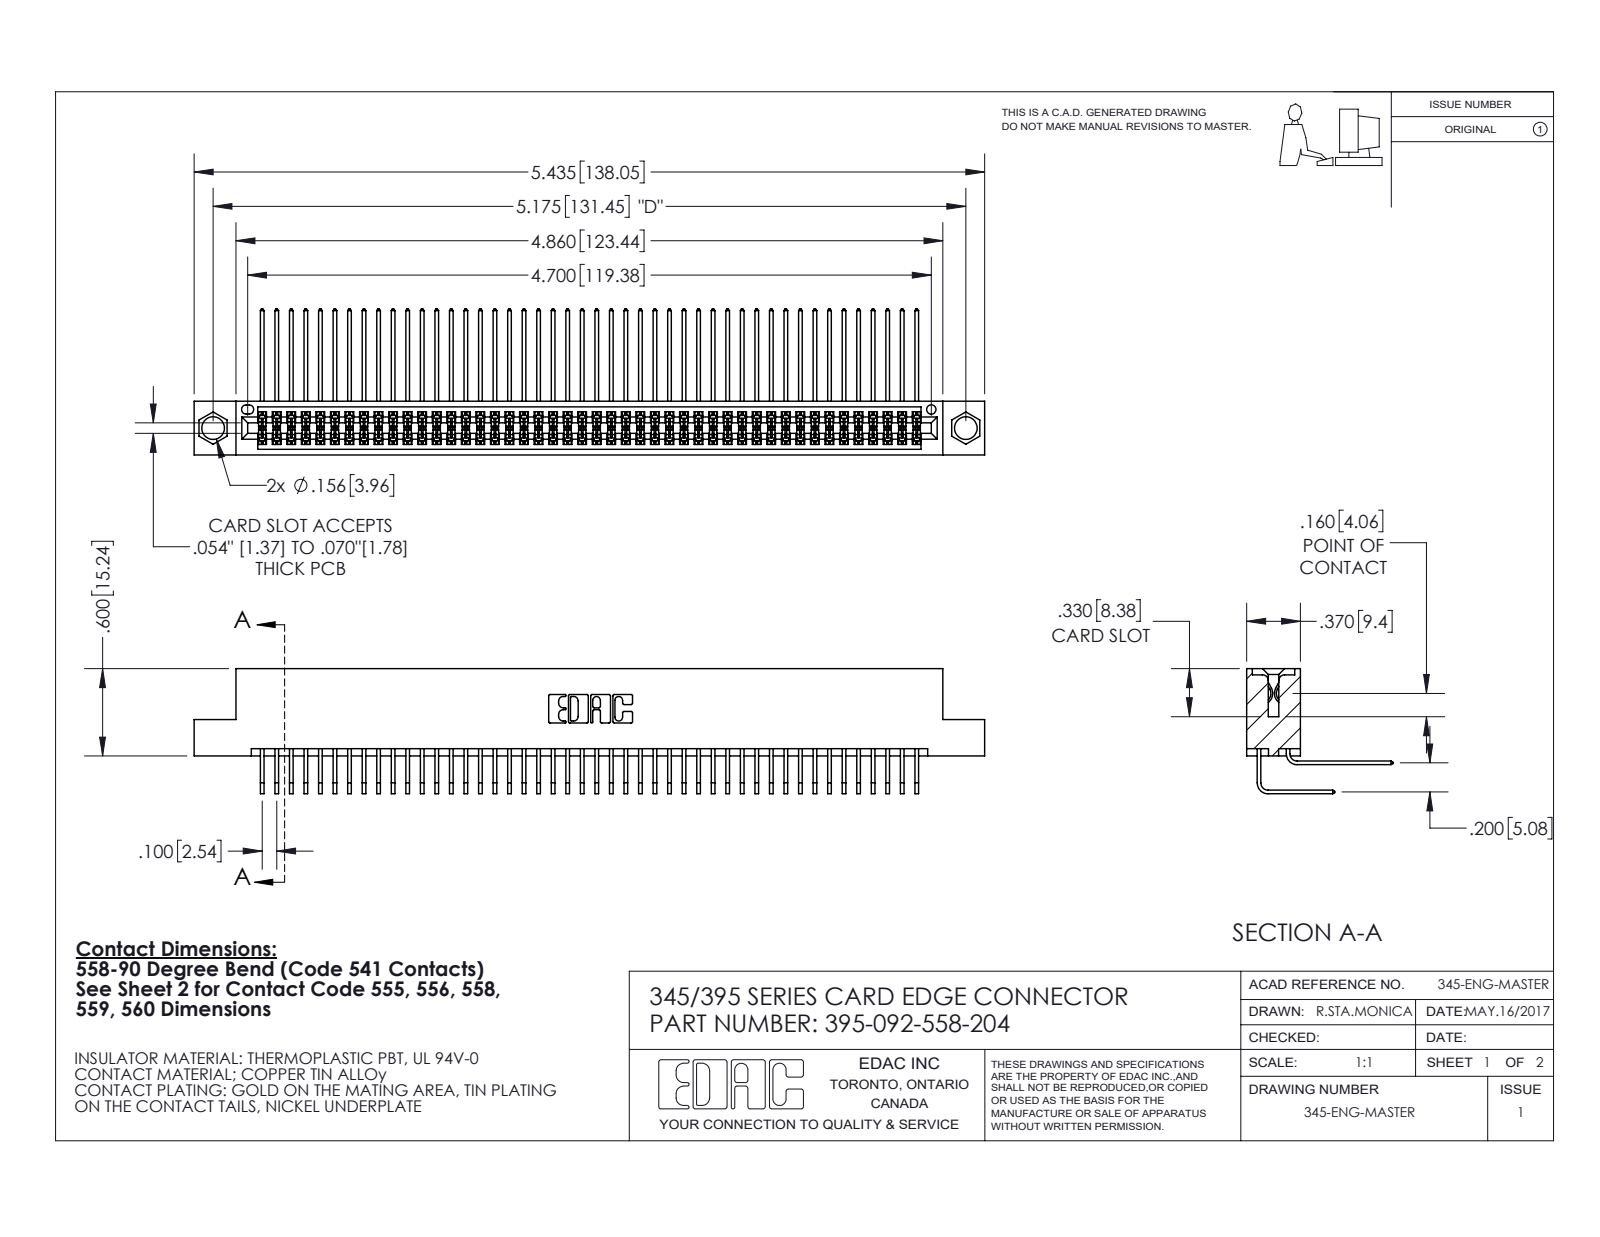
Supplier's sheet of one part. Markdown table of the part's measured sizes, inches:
| quantity | value |
| --- | --- |
| part name | 345-292-001_558 Tail - 2; 345-292-001_558 559 Tail - 1; 345 Part_Flush Mounting Lugs - 0.156 Dia-TI; 395-092-558-204 |
| STEP written by | SolidWorks 2020 (CONFIG_CONTROL_DESIGN) |
| units | inches |
| bodies | 93 solids, 4924 faces (3314 planar, 1610 cylindrical, 0 other) |
| overall size | 5.435 × 1.005 × 0.859 |
| volume | 0.847 in³ |
| surface area | 35.54 in² |
| round holes (diameter × count) | 0.156 × 2, 0.064 × 1 |
| partial cylindrical surfaces (radius × count) | 0.006 × 184, 0.01 × 22, 0.007 × 6, 0.031 × 6, 0.026 × 3, 0.014 × 2, 0.019 × 2, 0.022 × 2 |
| main face-to-face distances | 0.072, 0.298, 0.2, 0.37, 0.098, 0.272, 0.025, 0.225, 0.025, 0.175 |
| hole center spacings | 0.27, 4.939, 5.175 |
